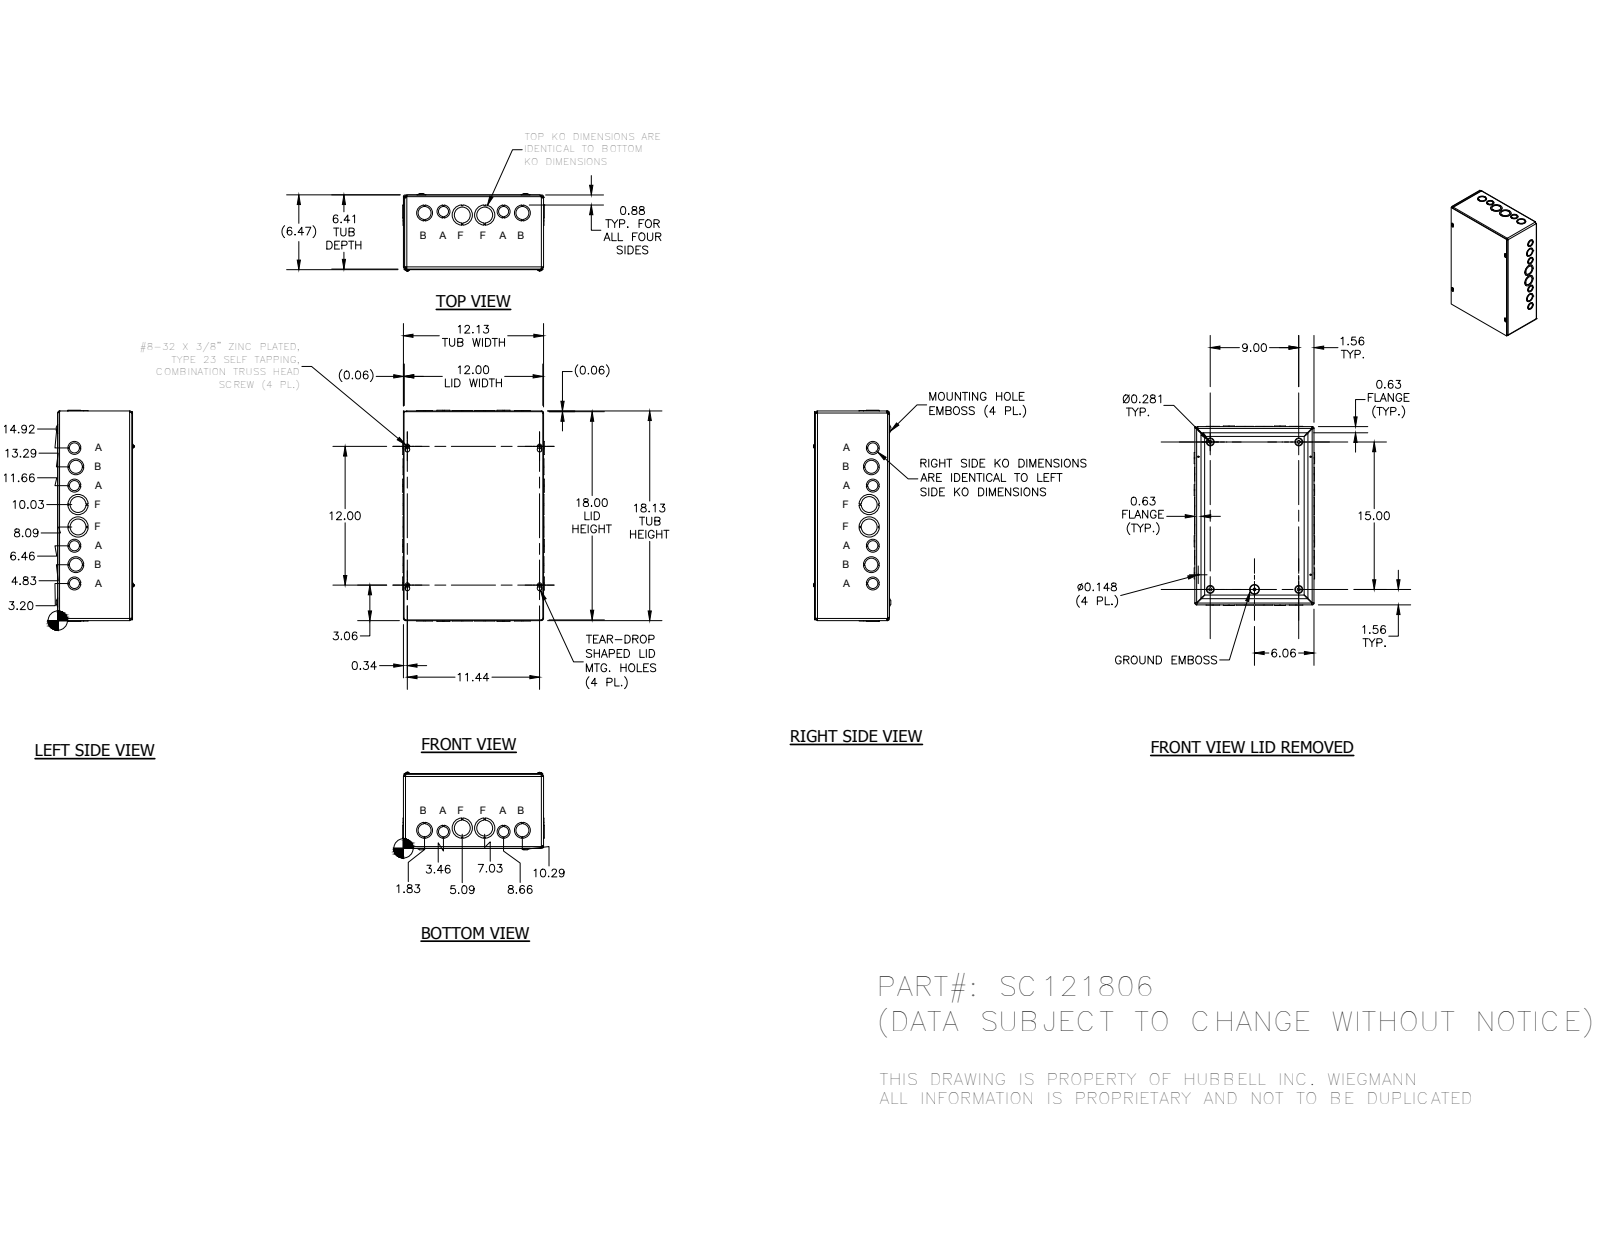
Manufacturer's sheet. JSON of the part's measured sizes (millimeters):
{"part_name": "SC1218BKP; SC121806WRA; SC1218LID; 34056 (+1 more)", "step_written_by": "Autodesk Inventor 2014 (AUTOMOTIVE_DESIGN)", "units": "millimeters", "bodies": {"solids": 30, "faces": 1142, "planar": 749, "cylindrical": 235, "other": 158}, "overall_size": [463.52, 311.12, 170], "round_holes": [[28.57, 10], [34.92, 8], [22.22, 6], [3.76, 4], [7.62, 4], [44.45, 4], [4.19, 1]], "round_bosses_or_shafts": [[9.75, 4], [4.17, 4], [5.8, 1]], "partial_cylinders_radius": [[3.17, 12], [4.75, 8], [1.4, 4], [1.57, 4], [2.38, 4], [2.97, 4], [3.15, 4], [3.96, 4]], "face_to_face_distances": [1.57, 161.12, 162.69, 1.59, 1.58, 162.71, 164.28, 307.98, 306.4, 306.41], "hole_center_spacings": [41.52, 42.15, 49.09, 82.94, 91.03, 132.17, 173.51, 344.29]}
